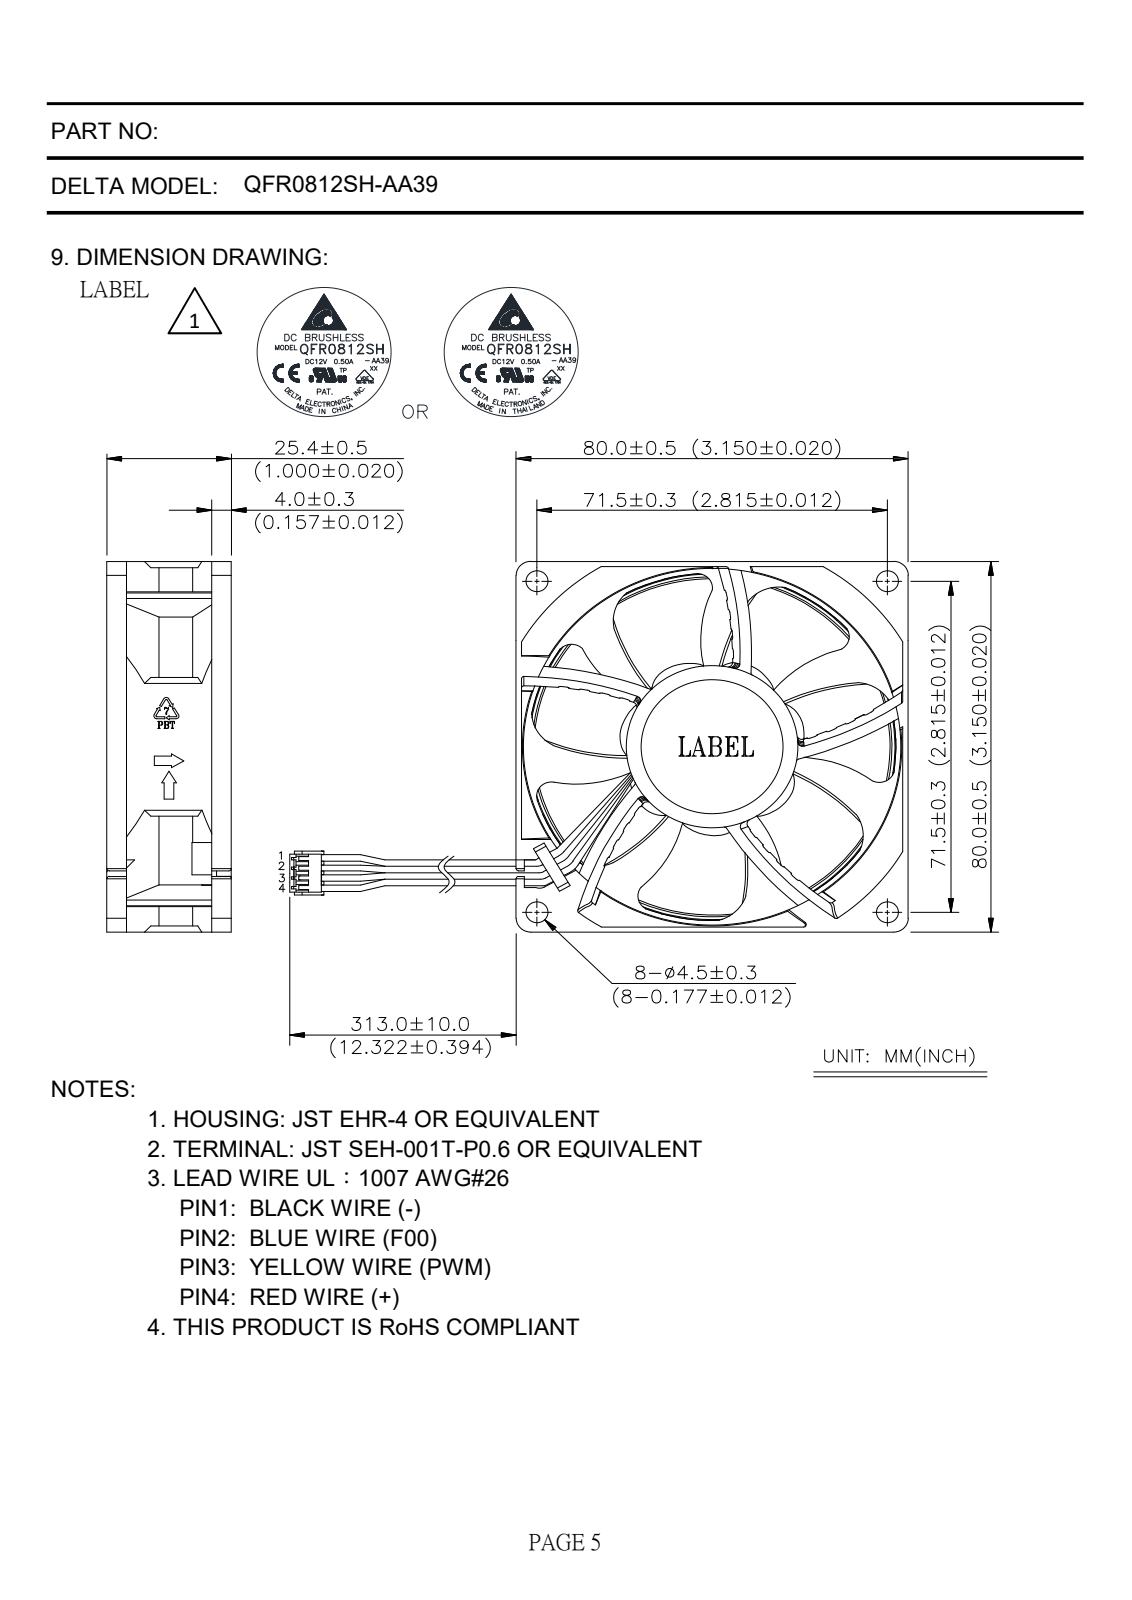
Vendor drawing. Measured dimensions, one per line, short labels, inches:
name: HUBB_1_1_1; 410200560000-ORING_7_1_1_1; QFR0812SH-AA39_REV000_STANDARD__ASM; QFR0812SH-AA39_REV0000_STANDARD_ASM
written by: CREO PARAMETRIC BY PTC INC, 2018400 (CONFIG_CONTROL_DESIGN)
unit: in
bodies: 2 solids, 856 faces (366 planar, 112 cylindrical, 378 other)
size: 3.165 × 3.15 × 1
volume: 2.861 in³; area: 51.54 in²
holes: 4× ⌀0.177, 1× ⌀3.016
bosses: 1× ⌀1.457, 1× ⌀1.378
rounds: 8× R0.02, 7× R0.316, 7× R0.77, 4× R0.033, 4× R0.118, 3× R0.006, 3× R0.007, 3× R0.024
face distances: 0.843, 3.15, 0.232, 0.051, 3.098, 0.61, 0.157, 3.047, 1, 0.768
hole spacings: 1.991, 2.815, 3.981
